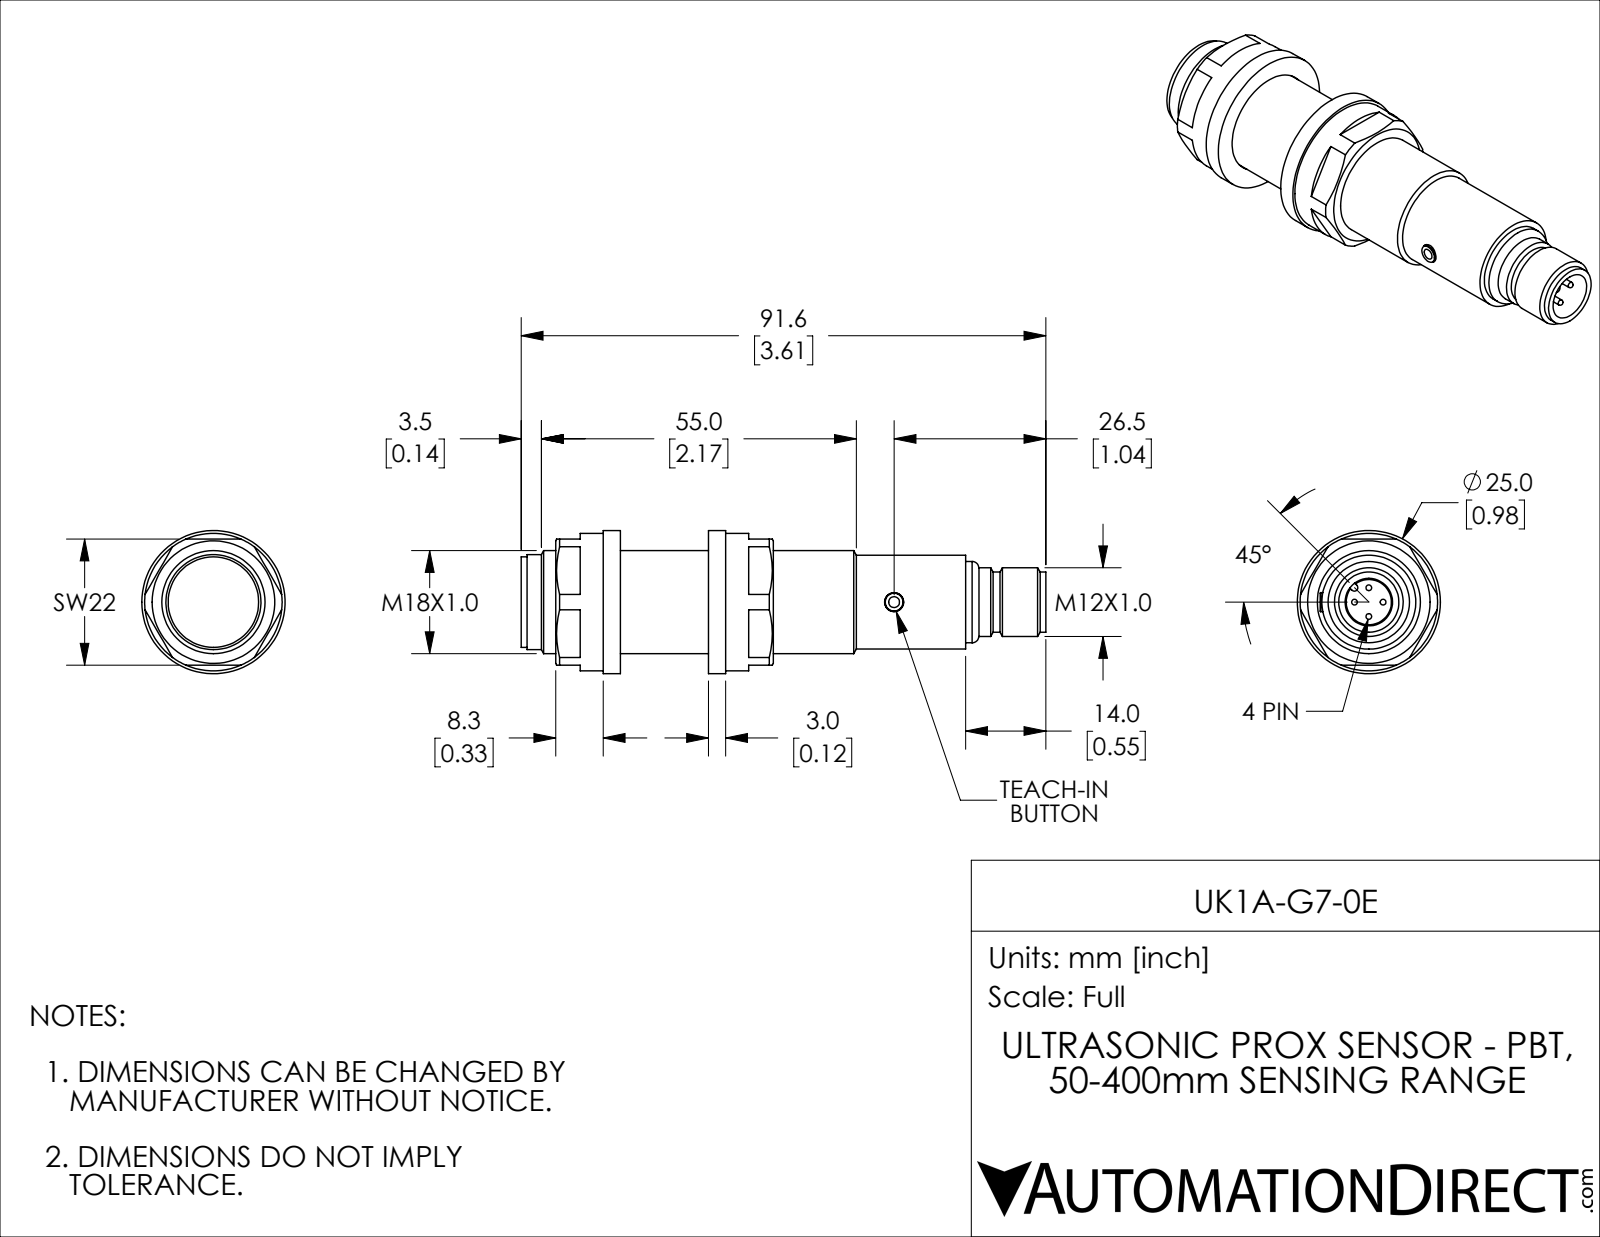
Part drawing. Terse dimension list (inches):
name: UK1A-G7-0E
written by: SolidWorks 2018 (AUTOMOTIVE_DESIGN)
unit: in
bodies: 6 solids, 123 faces (43 planar, 49 cylindrical, 31 other)
size: 3.606 × 0.984 × 0.984
volume: 1.477 in³; area: 16.01 in²
holes: 1× ⌀0.13, 1× ⌀0.327, 1× ⌀0.709, 1× ⌀0.717
bosses: 4× ⌀0.039, 1× ⌀0.984, 1× ⌀0.945, 1× ⌀0.654, 1× ⌀0.646, 1× ⌀0.622, 1× ⌀0.559, 1× ⌀0.472
rounds: 1× R0.024
face distances: 0.118, 0.724, 0.843, 0.606, 0.866, 0.327, 0.445, 1.051, 1.169, 0.563
